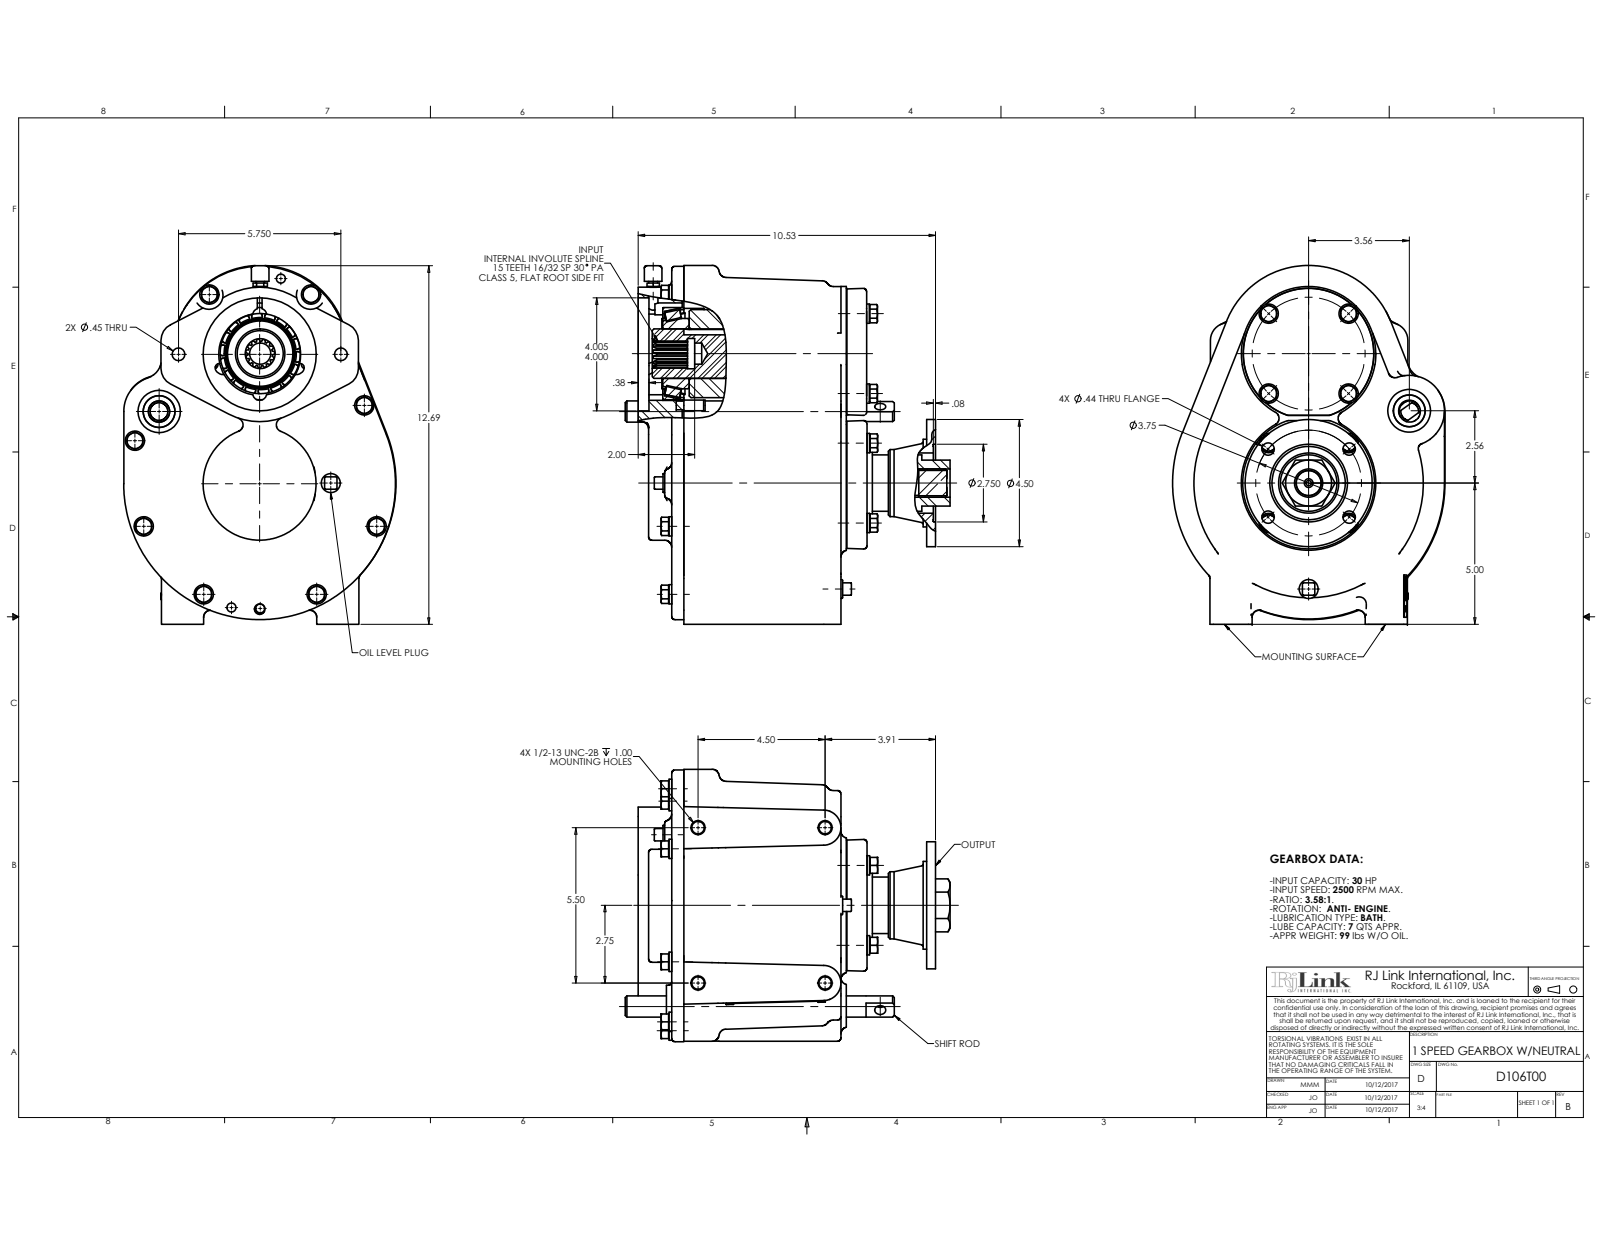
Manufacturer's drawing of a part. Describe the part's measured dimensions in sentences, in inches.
The part is named "D106021; D106023; DS90081A106_13; D106003 (+8 more)". Its 3-D file was written by "SolidWorks 2017 (AUTOMOTIVE_DESIGN)". It is 40 solids with 2841 faces: 1276 planar, 852 cylindrical and 713 other. Overall it measures 12.705 by 11.505 by 9.64 inches. Its volume is 174 cubic inches and its surface area 1 324 square inches. Round holes: 20 of diameter 0.32, 16 of diameter 0.382, 16 of diameter 0.406, 8 of diameter 0.422, 4 of diameter 0.437, 4 of diameter 0.44, 4 of diameter 3.264, 3 of diameter 0.188, 2 of diameter 0.125, 2 of diameter 0.37, 2 of diameter 0.375, 2 of diameter 0.375. Round bosses or shafts: 16 of diameter 0.683, 16 of diameter 0.561, 16 of diameter 0.375, 16 of diameter 0.312, 6 of diameter 0.375, 4 of diameter 0.5, 2 of diameter 4.62, 2 of diameter 1.501. Partial cylindrical surfaces (rounded edges, fillets, slot ends): 42 of radius 0.44, 28 of radius 0.25, 24 of radius 0.281, 16 of radius 0.03, 15 of radius 0.12, 12 of radius 1.25, 4 of radius 0.38, 4 of radius 0.62. The main face-to-face distances are 0.06, 0.43, 0.37, 5.813, 6.182, 5.752, 5.61, 5.24, 5.18, 0.572. The hole center spacings are 2, 2.828, 0.031, 4, 4.583, 3.47, 4.416, 4.684.
